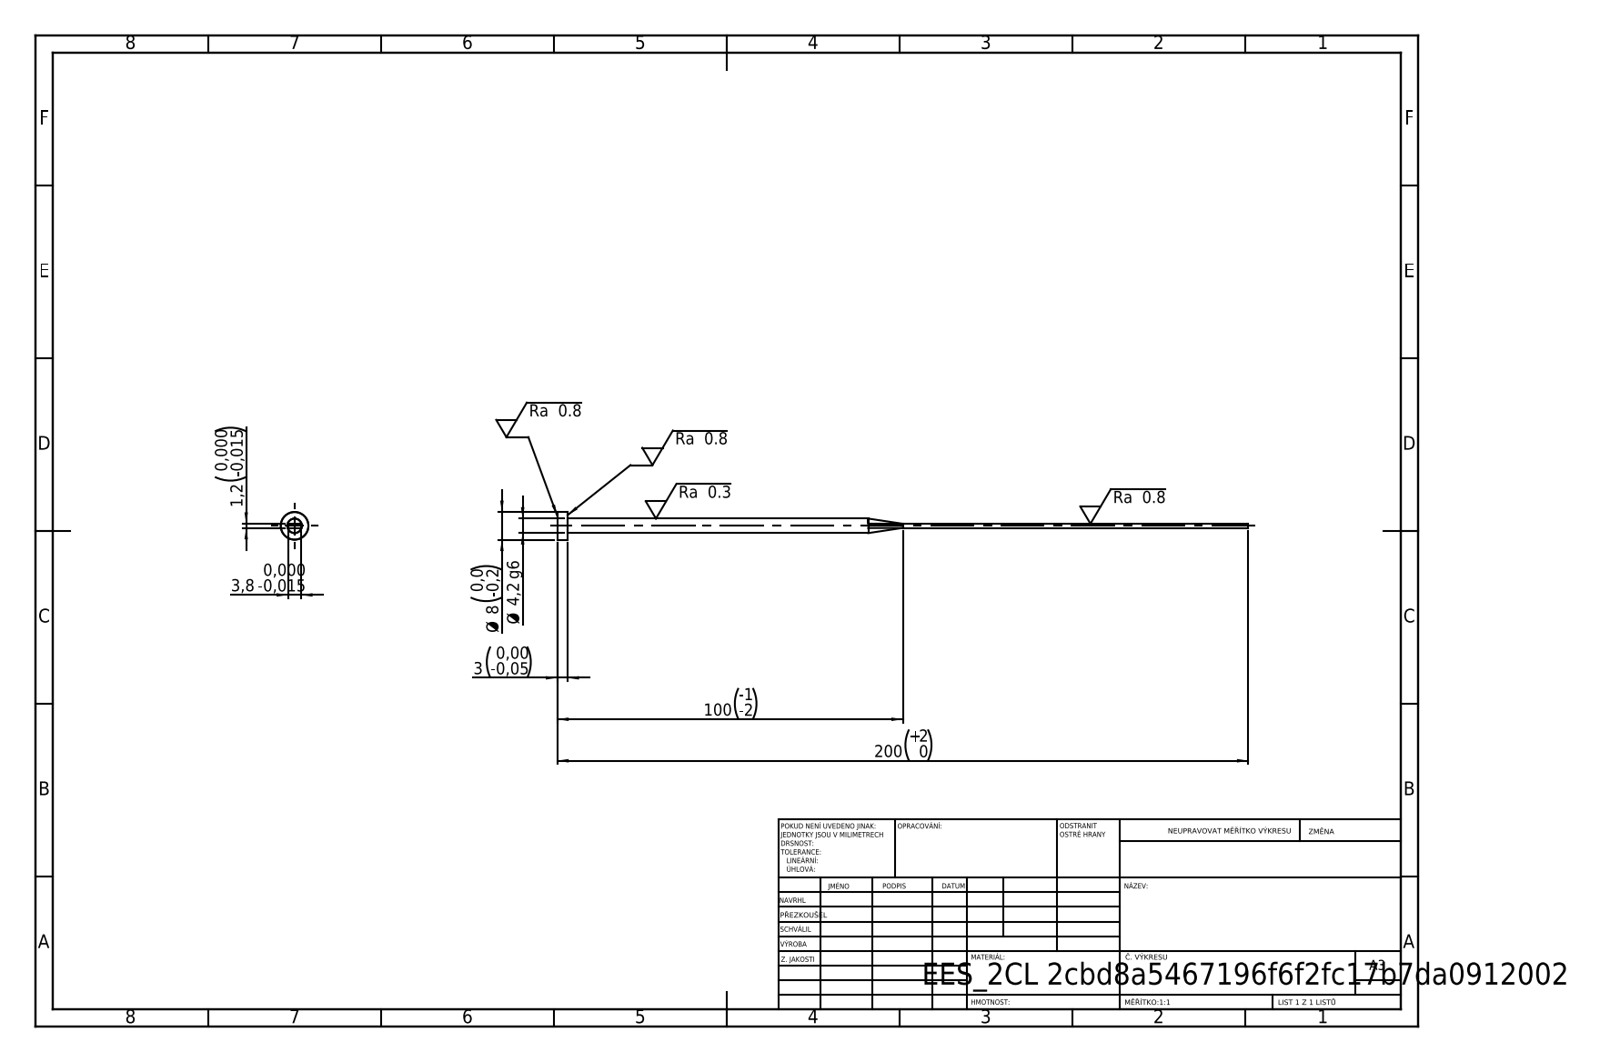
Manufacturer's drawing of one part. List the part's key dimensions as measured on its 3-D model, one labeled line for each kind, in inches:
STEP written by: SolidWorks 2019 (CONFIG_CONTROL_DESIGN)
Units: inches
Bodies: 1 solid, 15 faces (7 planar, 4 cylindrical, 4 other)
Overall size (bounding box): 7.874 × 0.315 × 0.315
Volume: 0.116 in³ · Surface area: 3.762 in²
Round bosses / shafts (diameter × count): ⌀0.315 ×1, ⌀0.165 ×1
Main face-to-face distances: 0.047, 0.15, 0.118, 7.874, 7.756
